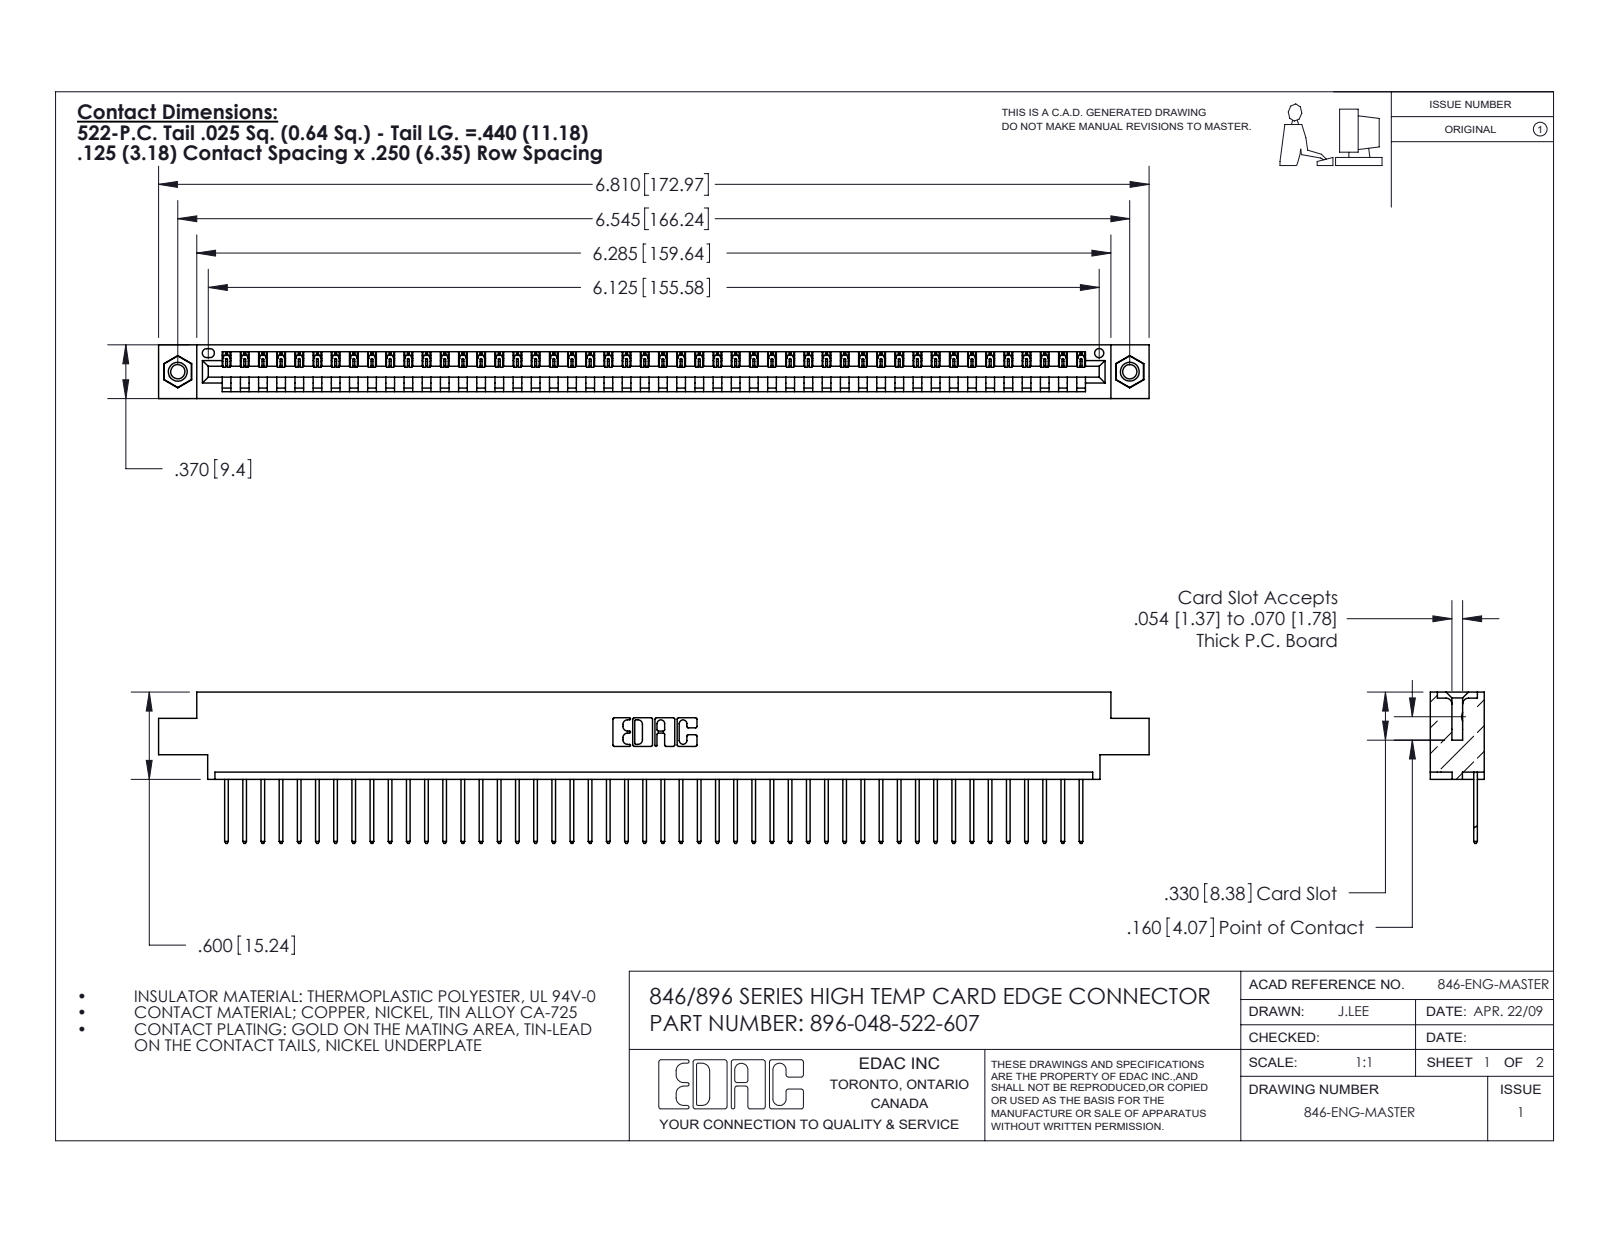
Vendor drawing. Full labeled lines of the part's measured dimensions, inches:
Part name (STEP PRODUCT): 346 Part_0.170 Offset - 0.156 Dia-TI; 396-048-522-607; 345-250-001_345-250-005-103; 345-292-001_345-293-122
STEP written by: SolidWorks 2016 (CONFIG_CONTROL_DESIGN)
Units: inches
Bodies: 51 solids, 2970 faces (2032 planar, 922 cylindrical, 16 other)
Overall size (bounding box): 6.81 × 1.04 × 0.37
Volume: 1.003 in³ · Surface area: 32.52 in²
Round holes (diameter × count): ⌀0.098 ×2, ⌀0.125 ×2, ⌀0.156 ×2, ⌀0.064 ×1
Round bosses / shafts (diameter × count): ⌀0.155 ×2
Partial cylindrical surfaces — rounded edges, fillets, slot ends (radius × count): R0.006 ×96, R0.01 ×96, R0.01 ×22, R0.007 ×6, R0.031 ×6, R0.026 ×3, R0.031 ×2, R0.04 ×2
Main face-to-face distances: 0.048, 0.322, 0.37, 0.25, 0.072, 0.298, 0.025, 0.222, 0.148, 0.1
Hole centre spacings: 0.246, 6.336, 6.545
